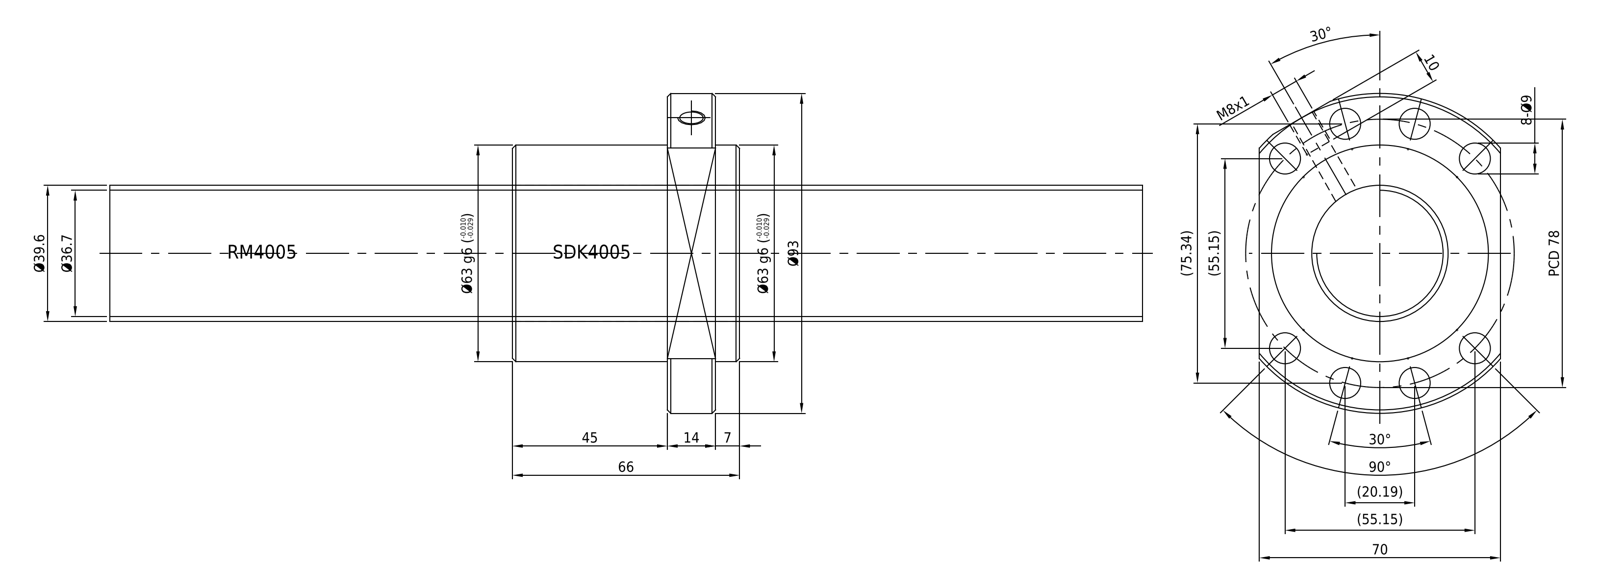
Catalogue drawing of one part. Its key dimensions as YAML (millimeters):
part_name: "SDK4005; RM4005"
step_written_by: "SolidWorks 2013 (CONFIG_CONTROL_DESIGN)"
units: millimeters
bodies: {solids: 2, faces: 52, planar: 9, cylindrical: 31, other: 12}
overall_size: [300, 93, 70]
volume: 522219
surface_area: 73788
round_holes:
  - {diameter: 9, count: 8}
  - {diameter: 3, count: 1}
  - {diameter: 6.8, count: 1}
  - {diameter: 40, count: 1}
round_bosses_or_shafts:
  - {diameter: 63, count: 1}
  - {diameter: 39.6, count: 1}
partial_cylinders:
  - {radius: 46.5, count: 1}
face_to_face_distances: [117, 183, 14, 7, 21, 66, 59, 45, 124, 138]
hole_center_spacings: [39, 75.34, 20.18, 67.55, 78, 20.19, 55.15, 55.16]
